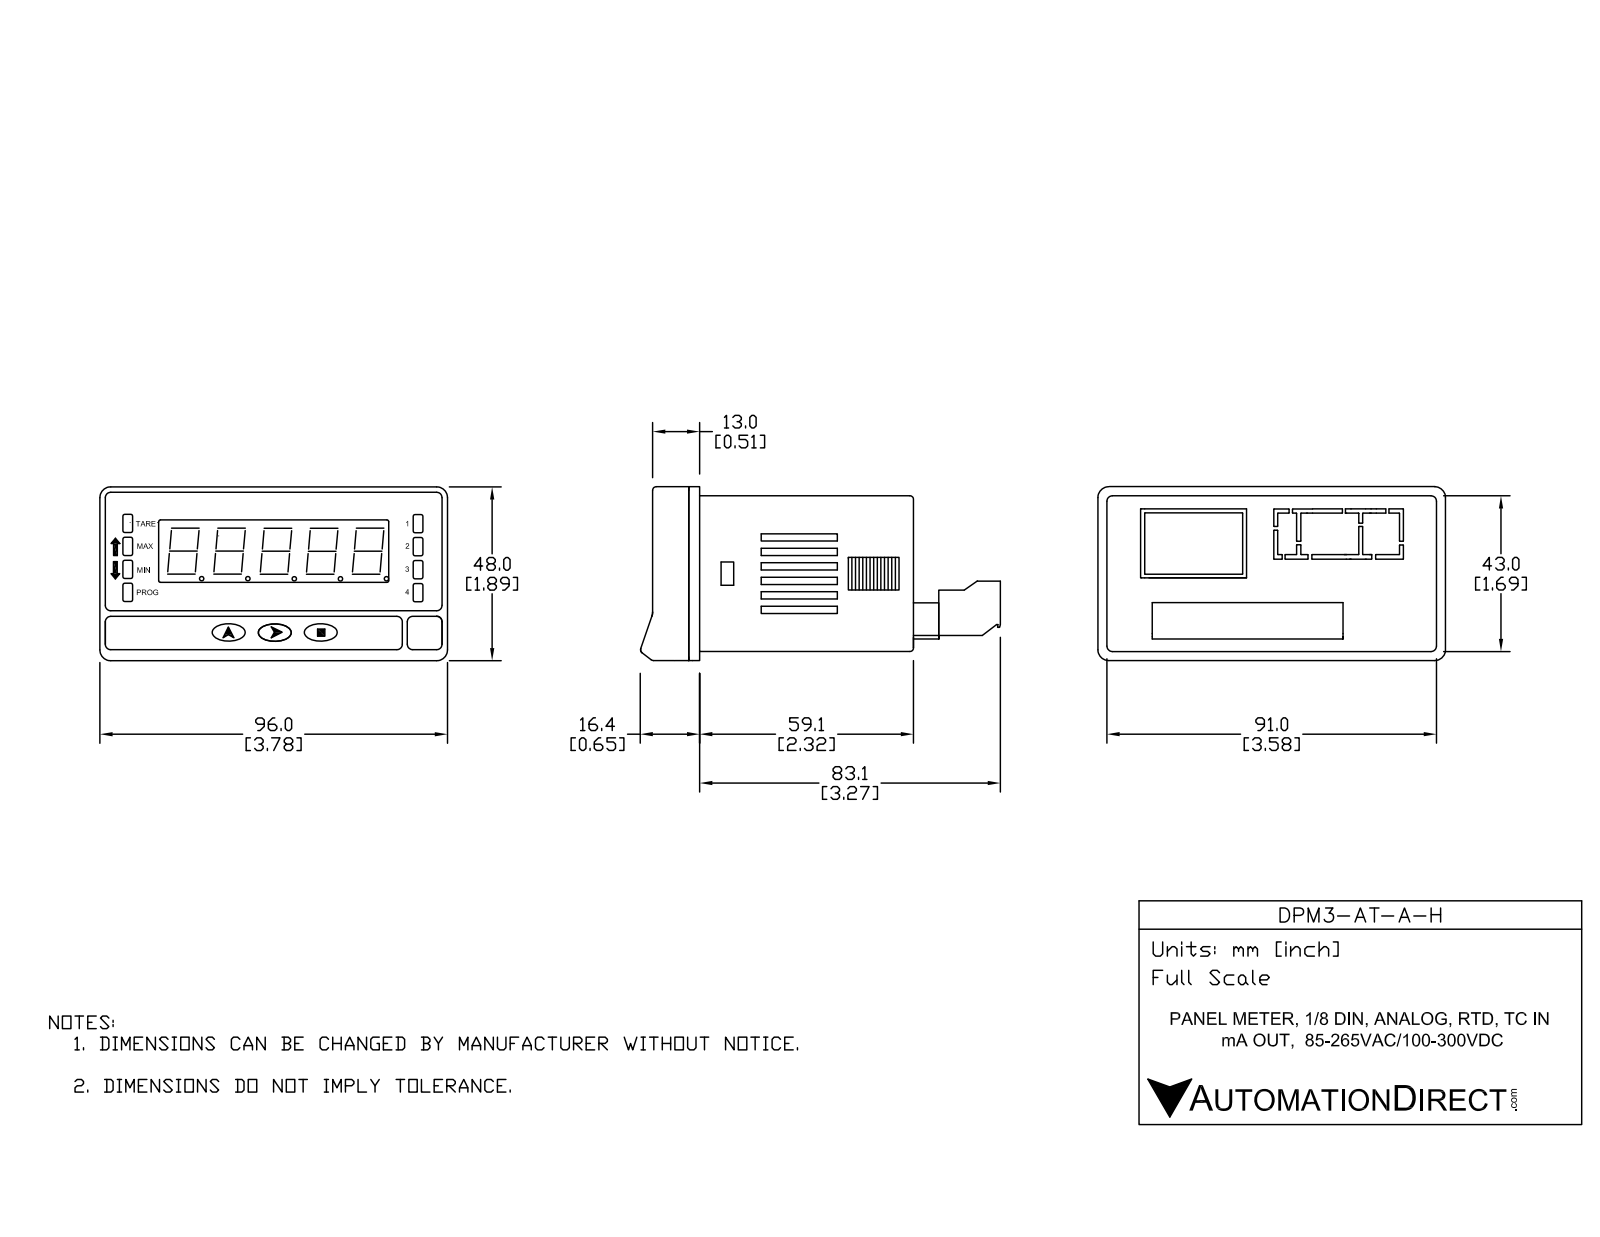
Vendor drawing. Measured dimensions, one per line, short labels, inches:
name: DPM3-AT-A-H
written by: SolidWorks 2017 (AUTOMOTIVE_DESIGN)
unit: in
bodies: 10 solids, 2622 faces (2041 planar, 368 cylindrical, 213 other)
size: 3.916 × 3.78 × 1.89
volume: 5.643 in³; area: 104.7 in²
holes: 12× ⌀0.039, 12× ⌀0.079, 10× ⌀0.078, 10× ⌀0.118, 10× ⌀0.152
bosses: 5× ⌀0.047
rounds: 53× R0.004, 42× R0.02, 24× R0.012, 24× R0.014, 12× R0.07, 12× R0.072, 10× R0.118, 10× R0.121
face distances: 0.059, 1.634, 0.098, 1.693, 1.575, 1.732, 3.524, 0.433, 0.157, 2.78
hole spacings: 0.138, 0.276, 0.201, 0.413, 0.748, 0.197, 0.197, 0.201
